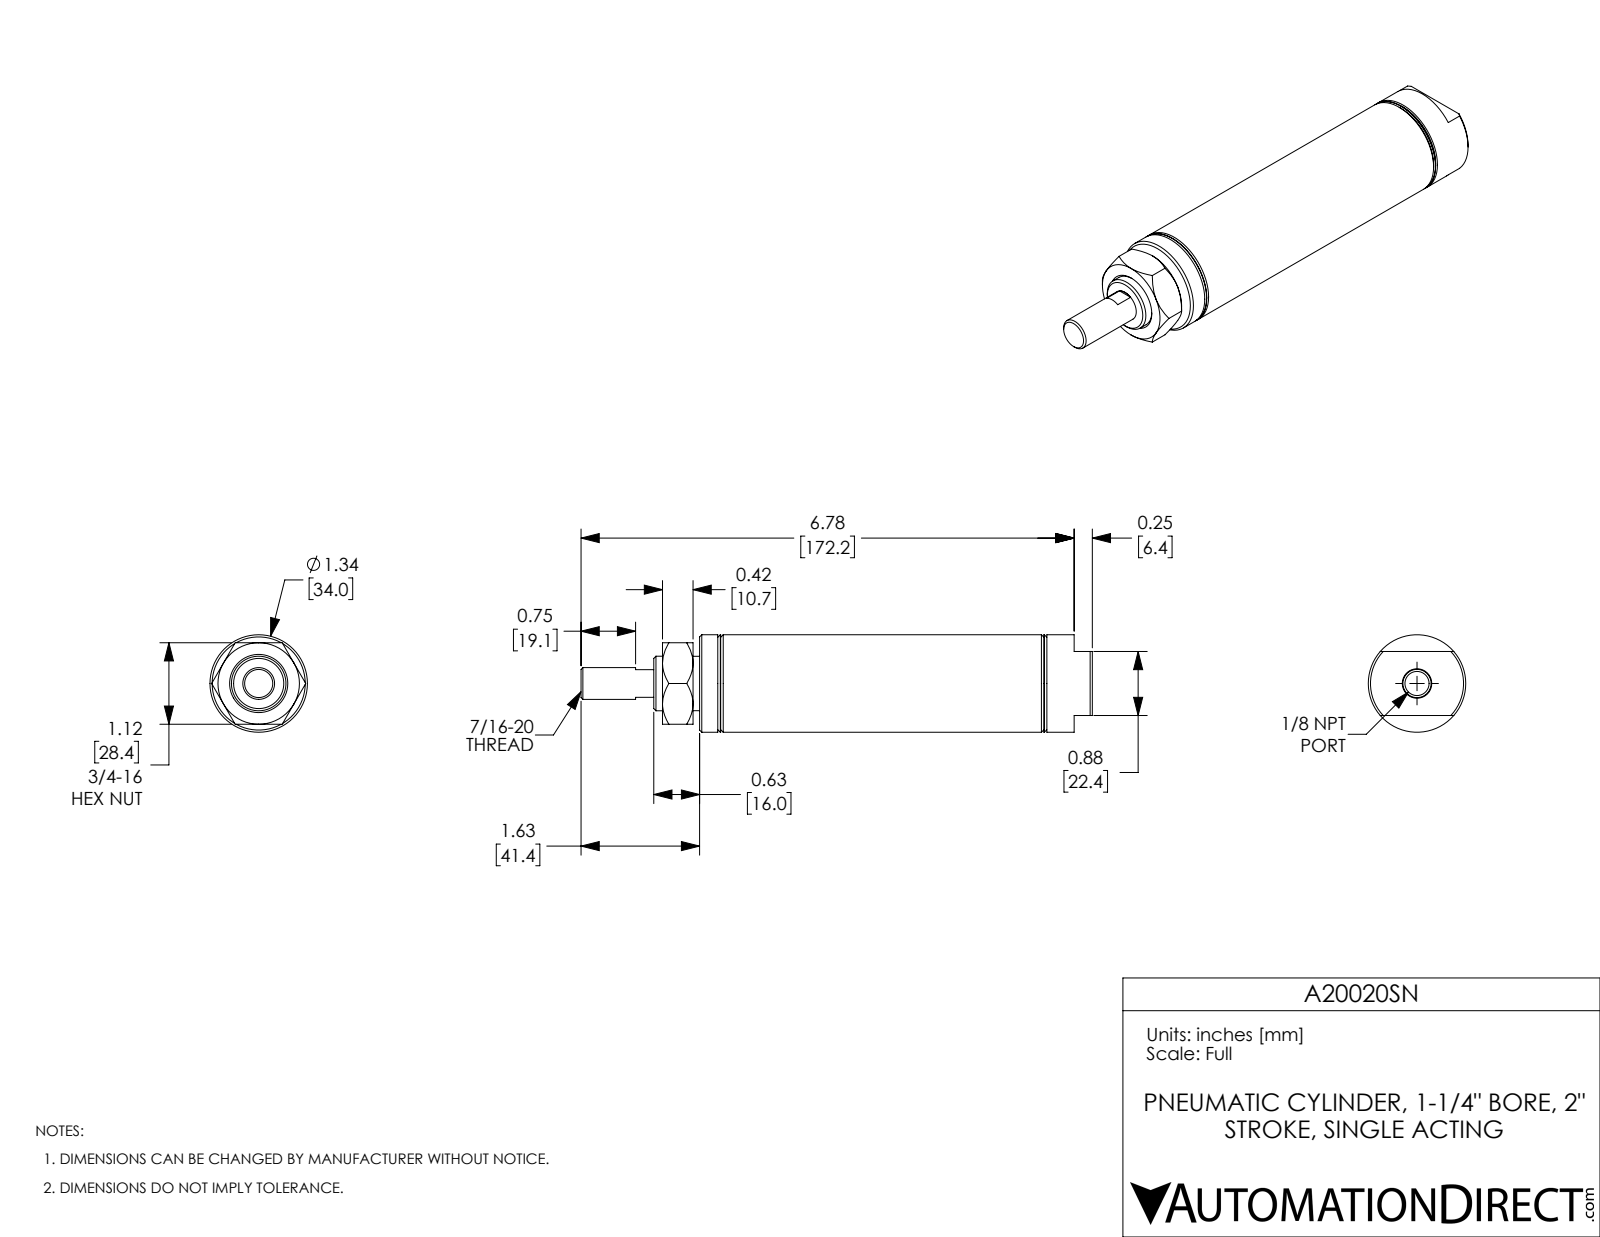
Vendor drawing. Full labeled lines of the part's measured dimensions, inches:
Part name (STEP PRODUCT): A20020SN; A20020SN_Mounting Nut_D-3556; A20020SN-Rod; A20020SN-MainBody
STEP written by: SolidWorks 2017 (AUTOMOTIVE_DESIGN)
Units: inches
Bodies: 3 solids, 95 faces (32 planar, 26 cylindrical, 37 other)
Overall size (bounding box): 7.03 × 1.34 × 1.34
Volume: 6.004 in³ · Surface area: 58.05 in²
Round holes (diameter × count): ⌀0.332 ×1, ⌀0.437 ×1, ⌀0.75 ×1, ⌀1.25 ×1
Round bosses / shafts (diameter × count): ⌀1.34 ×1, ⌀0.747 ×1
Main face-to-face distances: 1.45, 3.95, 2.5, 0.5, 2, 1.95, 5.4, 3.45, 1.12, 1
